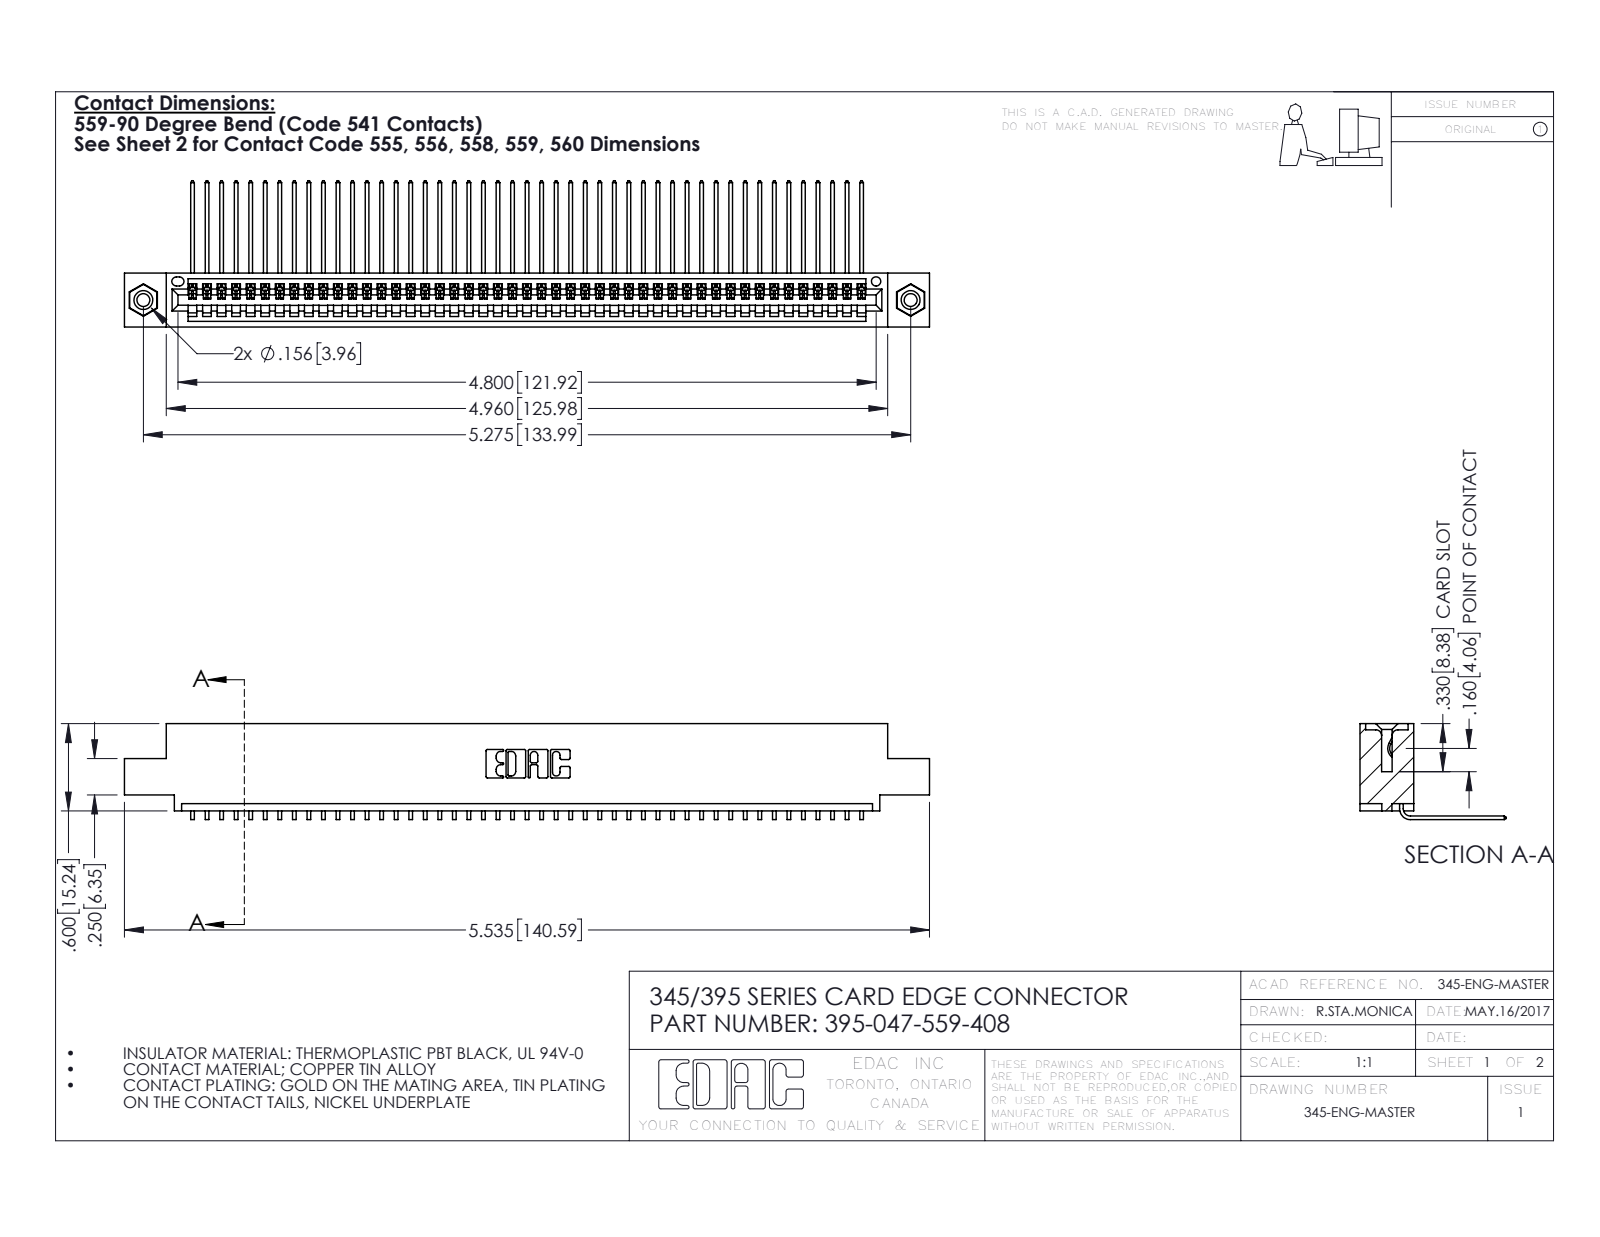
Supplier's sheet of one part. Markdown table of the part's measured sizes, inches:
| quantity | value |
| --- | --- |
| part name | 395-047-559-408; 345 Part_0.110 Offset - 0.156 Dia-TI; 345-250-001_345-250-003-102; 345-292-001_558 559 Tail - 1 |
| STEP written by | SolidWorks 2016 (CONFIG_CONTROL_DESIGN) |
| units | inches |
| bodies | 50 solids, 3010 faces (2090 planar, 904 cylindrical, 16 other) |
| overall size | 5.535 × 1.005 × 0.659 |
| volume | 0.822 in³ |
| surface area | 29.44 in² |
| round holes (diameter × count) | 0.089 × 2, 0.125 × 2, 0.156 × 2, 0.064 × 1 |
| round bosses / shafts (diameter × count) | 0.155 × 2 |
| partial cylindrical surfaces (radius × count) | 0.006 × 94, 0.01 × 22, 0.007 × 6, 0.031 × 6, 0.026 × 3, 0.031 × 2, 0.04 × 2, 0.014 × 1 |
| main face-to-face distances | 0.072, 0.298, 0.37, 0.2, 0.098, 0.272, 0.025, 0.225, 0.149, 0.072 |
| hole center spacings | 0.27, 5.039, 5.275 |
